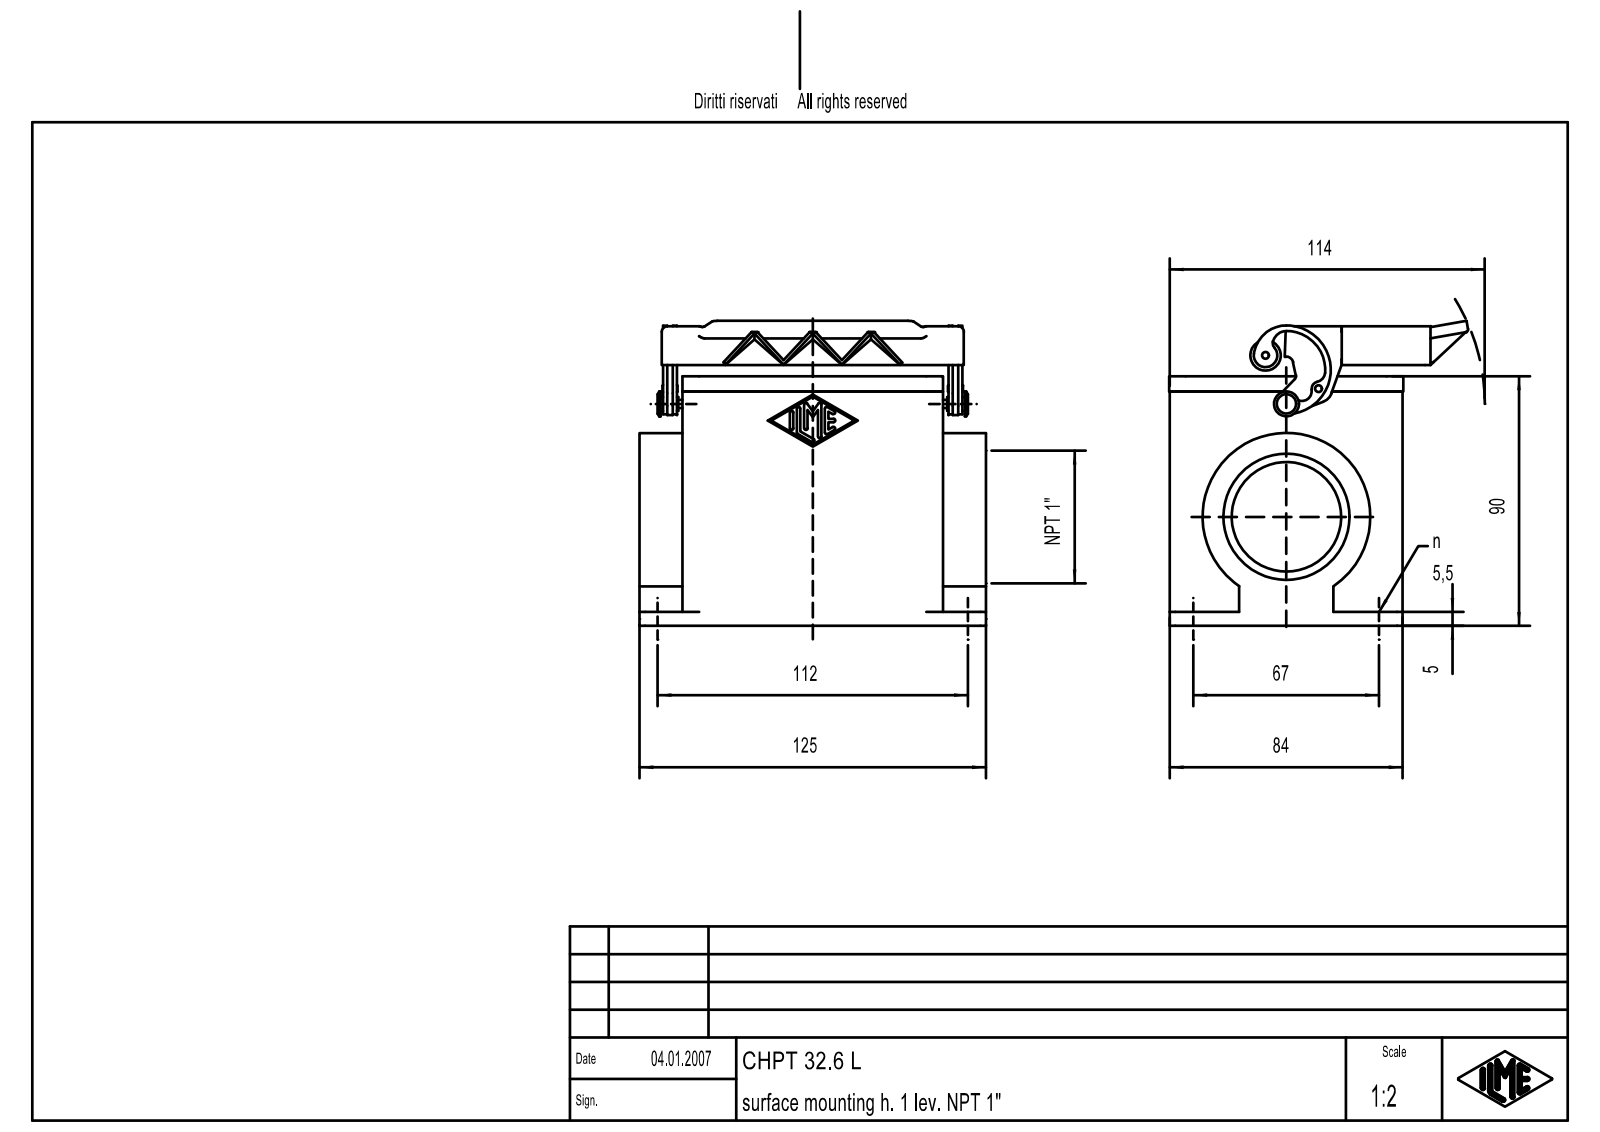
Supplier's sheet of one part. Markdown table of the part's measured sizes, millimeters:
| quantity | value |
| --- | --- |
| part name | MSBO8171 |
| STEP written by | Creo Elements/Direct Modeling 18.0B 02-Dec-2011 (C) Parametric Technology GmbH (AUTOMOTIVE_DESIGN) |
| units | millimeters |
| bodies | 1 solid, 409 faces (193 planar, 172 cylindrical, 44 other) |
| overall size | 125 × 109.98 × 107.59 |
| volume | 270 580 mm³ |
| surface area | 100 080 mm² |
| round holes (diameter × count) | 2.46 × 8, 3 × 8, 5.5 × 4, 39.48 × 1, 45.48 × 1 |
| round bosses / shafts (diameter × count) | 60.5 × 1, 11 × 1, 9 × 1, 5 × 1, 3 × 1 |
| partial cylindrical surfaces (radius × count) | 0.62 × 14, 2 × 12, 1.5 × 9, 0.14 × 4, 3 × 4, 6 × 4, 1 × 3, 2.5 × 3 |
| main face-to-face distances | 3, 81, 4, 84, 78, 11.5, 82.5, 98, 71, 27 |
| hole center spacings | 17.37, 27, 33.74, 36, 41.73, 67.25, 77.5, 82.07 |
